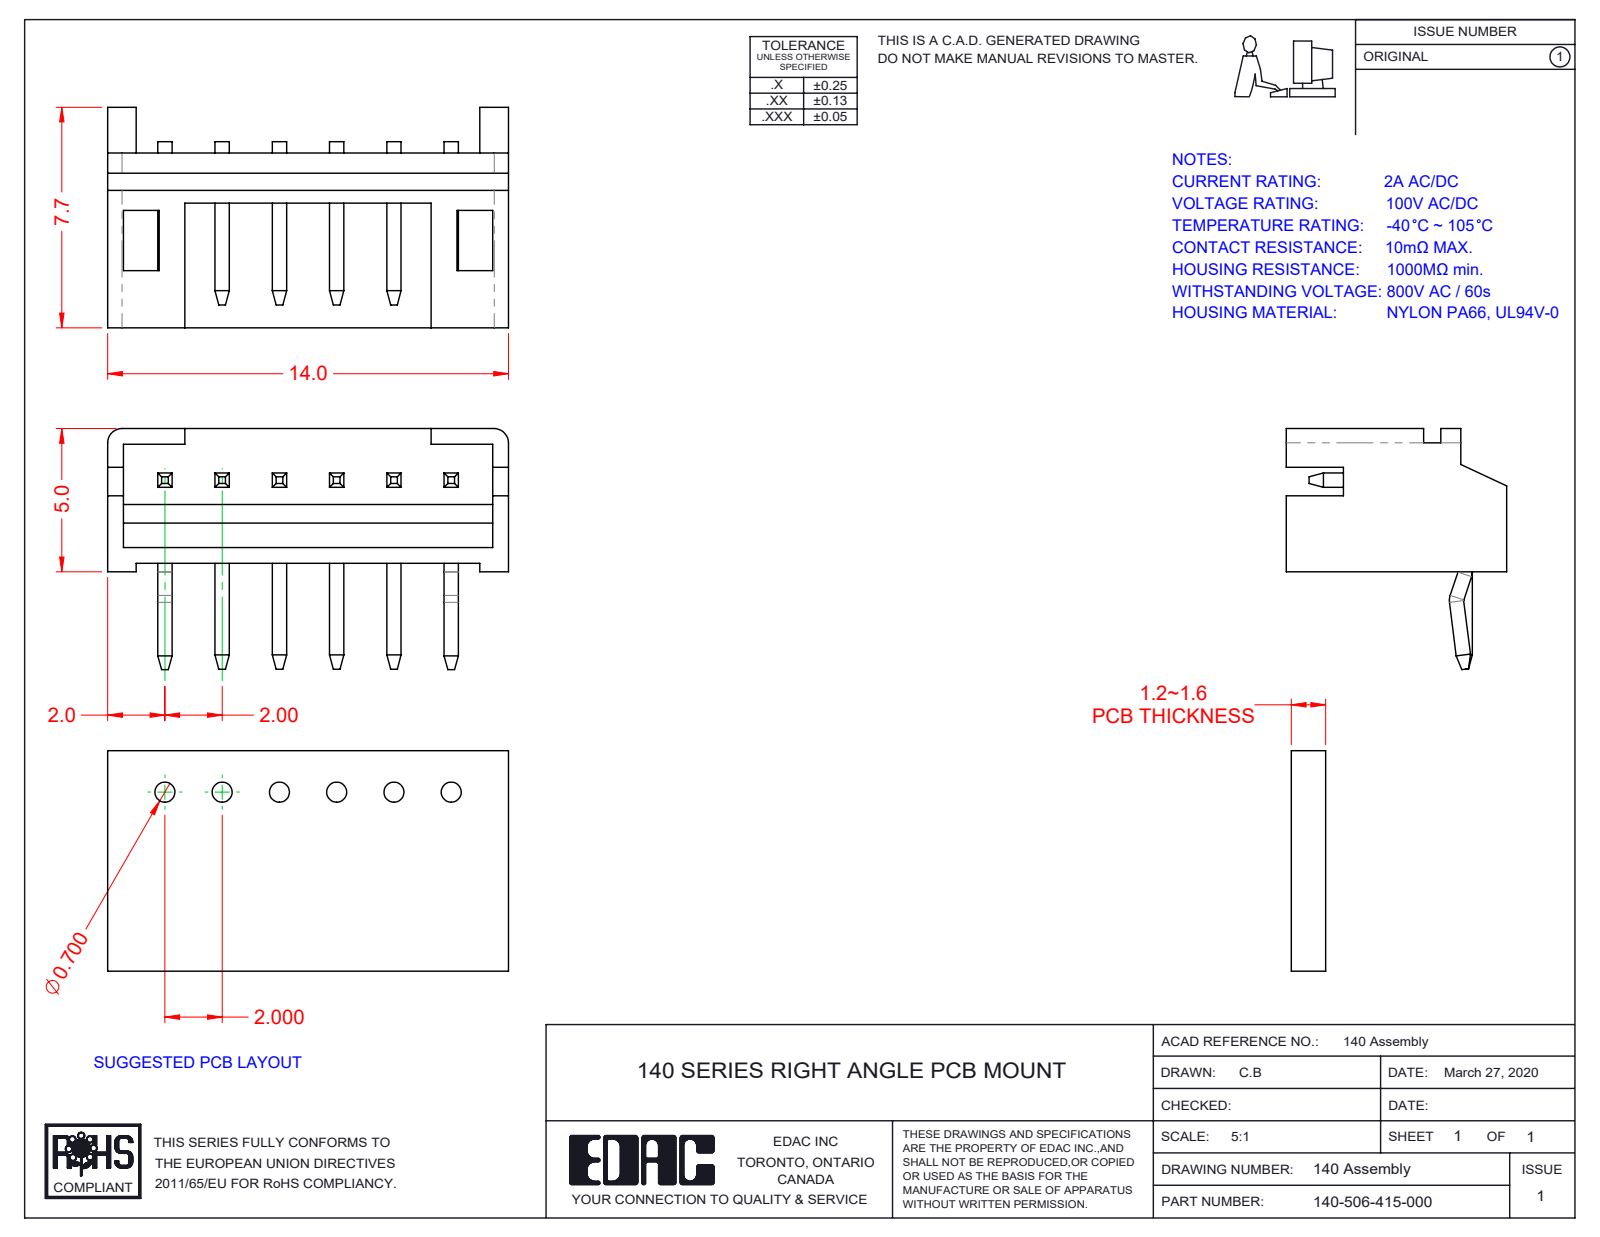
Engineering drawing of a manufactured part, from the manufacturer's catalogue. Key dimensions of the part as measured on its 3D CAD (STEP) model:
Part name (STEP PRODUCT): 140-506-415-000; RA Housing_506; RA Contact_Kink; RA Contact_Str
STEP written by: SolidWorks 2016 (CONFIG_CONTROL_DESIGN)
Units: millimetres
Bodies: 7 solids, 259 faces (235 planar, 24 cylindrical, 0 other)
Overall size (bounding box): 14 × 8.41 × 7.7
Volume: 179 mm³ · Surface area: 654 mm²
Partial cylindrical surfaces — rounded edges, fillets, slot ends (radius × count): R0.5 ×2, R0.55 ×2, R0.15 ×1, R0.65 ×1
Main face-to-face distances: 0.55, 1.5, 0.5, 2, 4, 6, 1, 4.15, 1.75, 4.5
